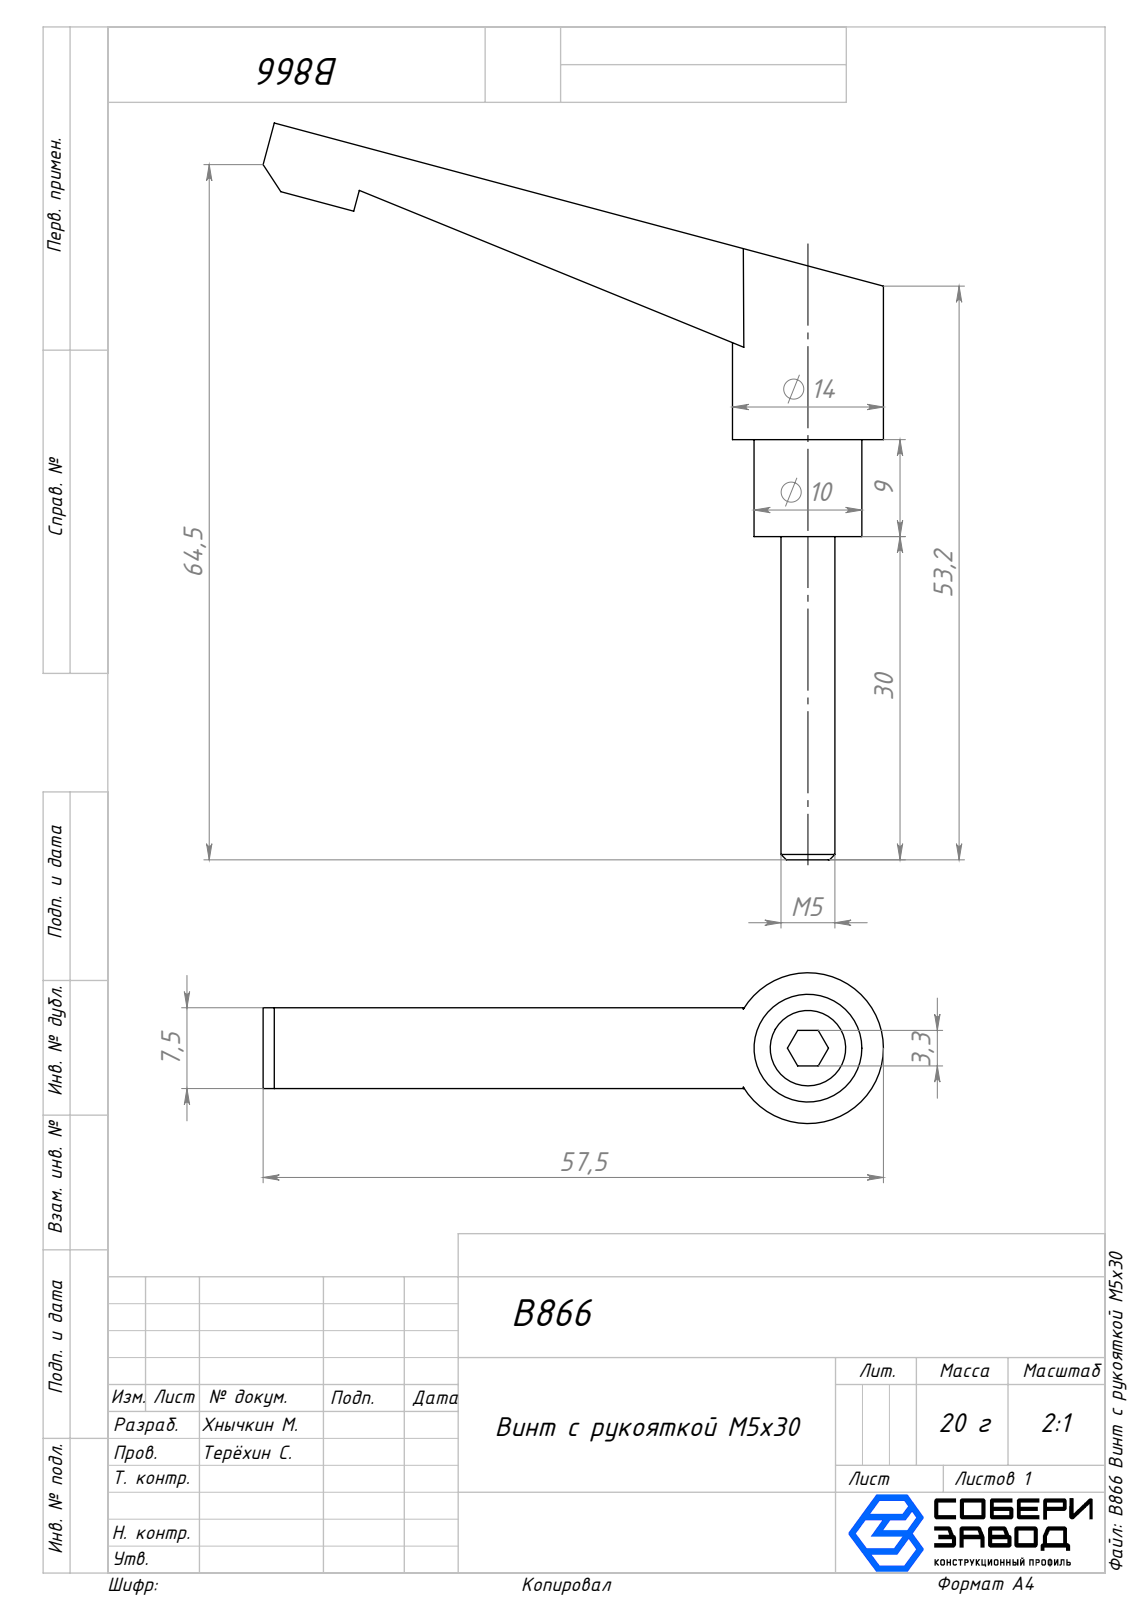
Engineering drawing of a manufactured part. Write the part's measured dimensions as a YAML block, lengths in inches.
part_name: "Винт с рукояткой_00; B866 Винт с рукояткой М5х30; Рукоятка_00; Винтик_00"
step_written_by: "SolidWorks 2025 (AUTOMOTIVE_DESIGN)"
units: inches
bodies: {solids: 3, faces: 52, planar: 32, cylindrical: 18, other: 2}
overall_size: [2.693, 2.265, 0.551]
volume: 0.298
surface_area: 7.113
round_holes:
  - {diameter: 0.118, count: 1}
  - {diameter: 0.236, count: 1}
  - {diameter: 0.394, count: 1}
round_bosses_or_shafts:
  - {diameter: 0.551, count: 1}
  - {diameter: 0.276, count: 1}
  - {diameter: 0.197, count: 1}
face_to_face_distances: [0.039, 0.295, 0.256, 0.217, 0.138, 0.394, 0.433, 0.354, 0.748, 0.787]
